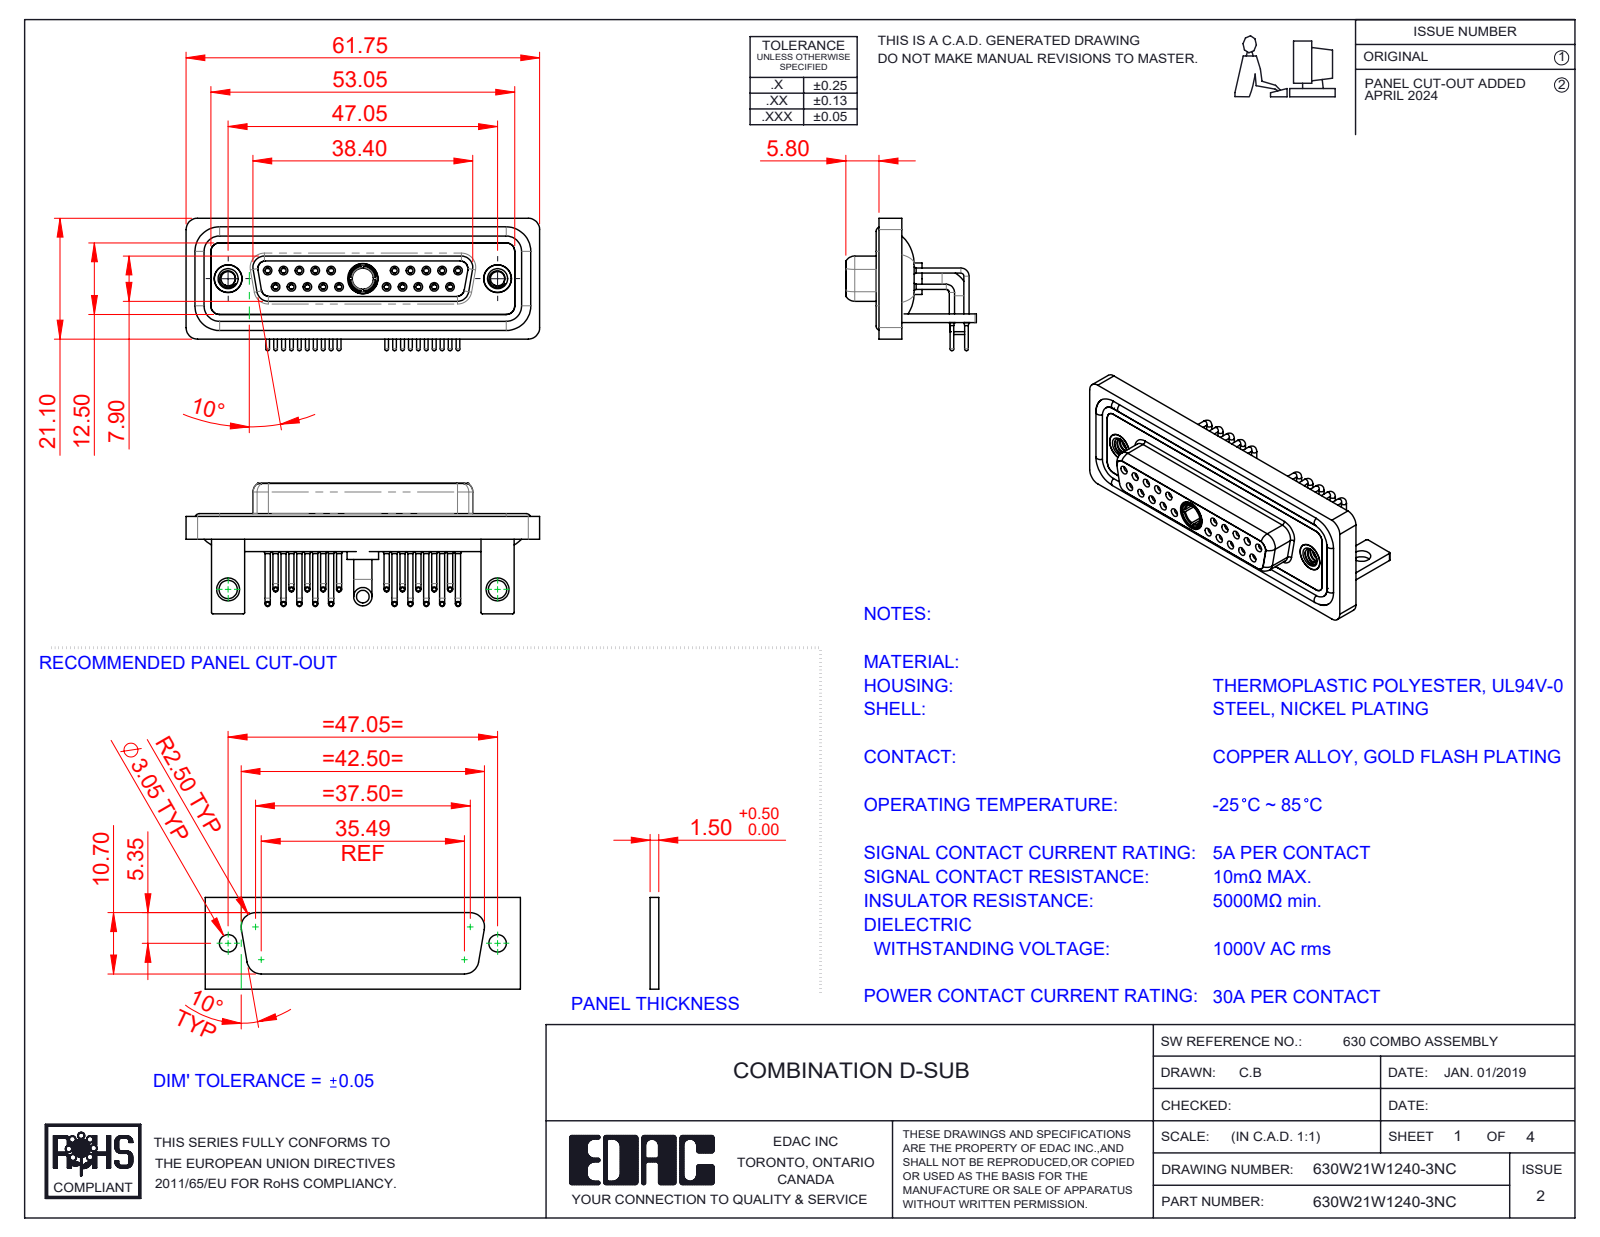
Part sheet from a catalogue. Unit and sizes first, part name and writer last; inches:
Units: inches
Overall size (bounding box): 2.431 × 0.91 × 0.898
Round holes (diameter × count): ⌀0.035 ×20, ⌀0.043 ×20, ⌀0.059 ×20, ⌀0.079 ×20, ⌀0.063 ×10, ⌀0.067 ×10, ⌀0.191 ×3, ⌀0.098 ×2, ⌀0.126 ×2, ⌀0.157 ×2, ⌀0.159 ×2, ⌀0.197 ×2
Round bosses / shafts (diameter × count): ⌀0.035 ×20, ⌀0.026 ×20, ⌀0.063 ×14, ⌀0.195 ×2, ⌀0.189 ×2, ⌀0.126 ×2, ⌀0.217 ×1, ⌀0.205 ×1
Partial cylindrical surfaces — rounded edges, fillets, slot ends (radius × count): R0.079 ×19, R0.059 ×18, R0.01 ×16, R0.053 ×8, R0.063 ×8, R0.02 ×5, R0.024 ×4, R0.026 ×4
Main face-to-face distances: 0.016, 0.071, 0.114, 0.146, 0.059, 0.161, 0.043, 0.055, 0.063, 0.098
Hole centre spacings: 0.124, 0.109, 0.218, 0.327, 0.198, 0.763, 0.826, 0.872
Volume: 0.543 in³ · Surface area: 24.08 in²
Bodies: 31 solids, 1566 faces (454 planar, 695 cylindrical, 417 other)
Part name (STEP PRODUCT): 630Combo Waterproof Housing_25 Contacts; 630Combo Housing_21W1; Power Socket_30A RA; 630Combo Shell Rear_25 Contacts (+6 more)
STEP written by: SolidWorks 2023 (CONFIG_CONTROL_DESIGN)
